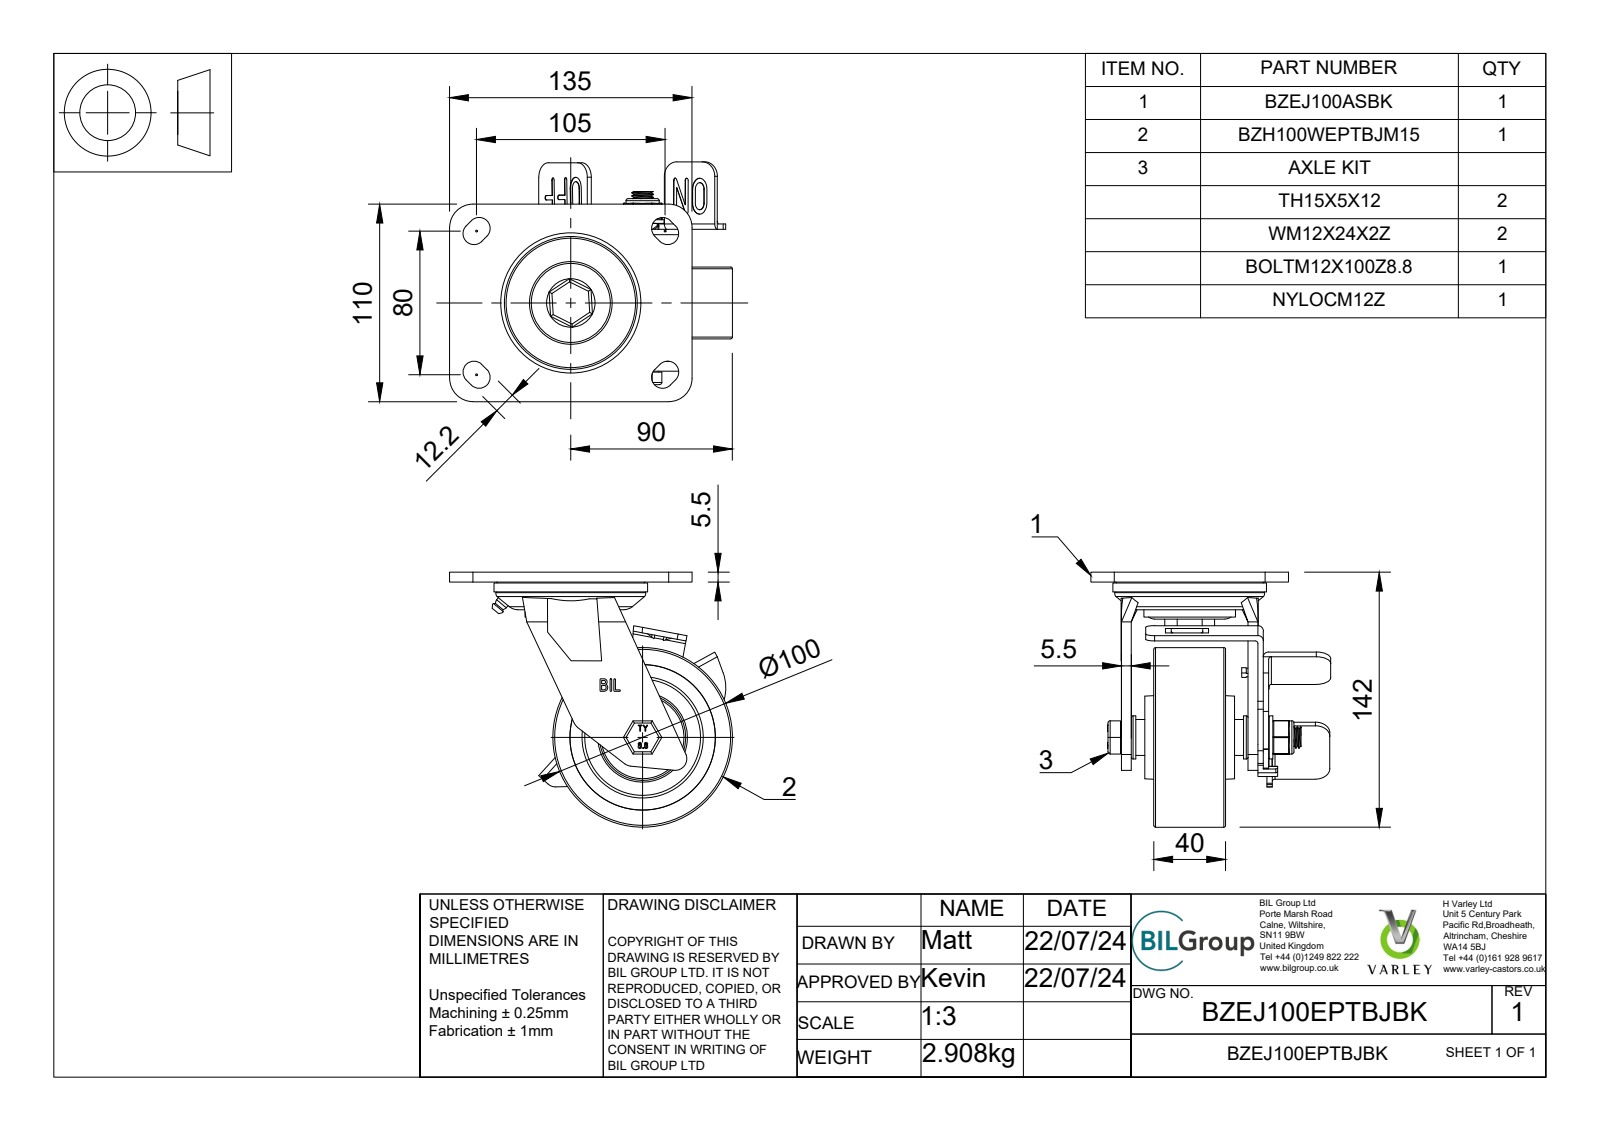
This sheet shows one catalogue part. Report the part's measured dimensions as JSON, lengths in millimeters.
{"part_name": "BZEJ100EPTBJBK v4; BZEJ100ASBK v1; FABRICATED STEEL TOP PLATE; FABRICATED STEEL TOP PLATE Geometry (+8 more)", "step_written_by": "Autodesk Translation Framework v13.14.0.145 (AUTOMOTIVE_DESIGN)", "units": "millimeters", "bodies": {"solids": 49, "faces": 1466, "planar": 564, "cylindrical": 328, "other": 574}, "overall_size": [157.5, 142, 133.5], "volume_mm3": 520171, "surface_area_mm2": 198808, "round_holes": [[12, 1], [12.5, 1], [13, 1], [14, 1], [15, 1], [16, 1], [16.5, 1], [18, 1], [20.5, 1], [26, 1], [26.8, 1], [28, 1]], "round_bosses_or_shafts": [[100, 1], [85.5, 1], [51, 1], [24, 1], [23, 1], [21.5, 1], [20, 1], [19, 1]], "partial_cylinders_radius": [[0.5, 30], [1.5, 13], [6.1, 8], [1.25, 6], [6, 5], [3, 4], [5, 4], [8, 4]], "face_to_face_distances": [5.5, 3, 18, 70.5, 12.5, 52.5, 58, 0.5, 6, 5]}
